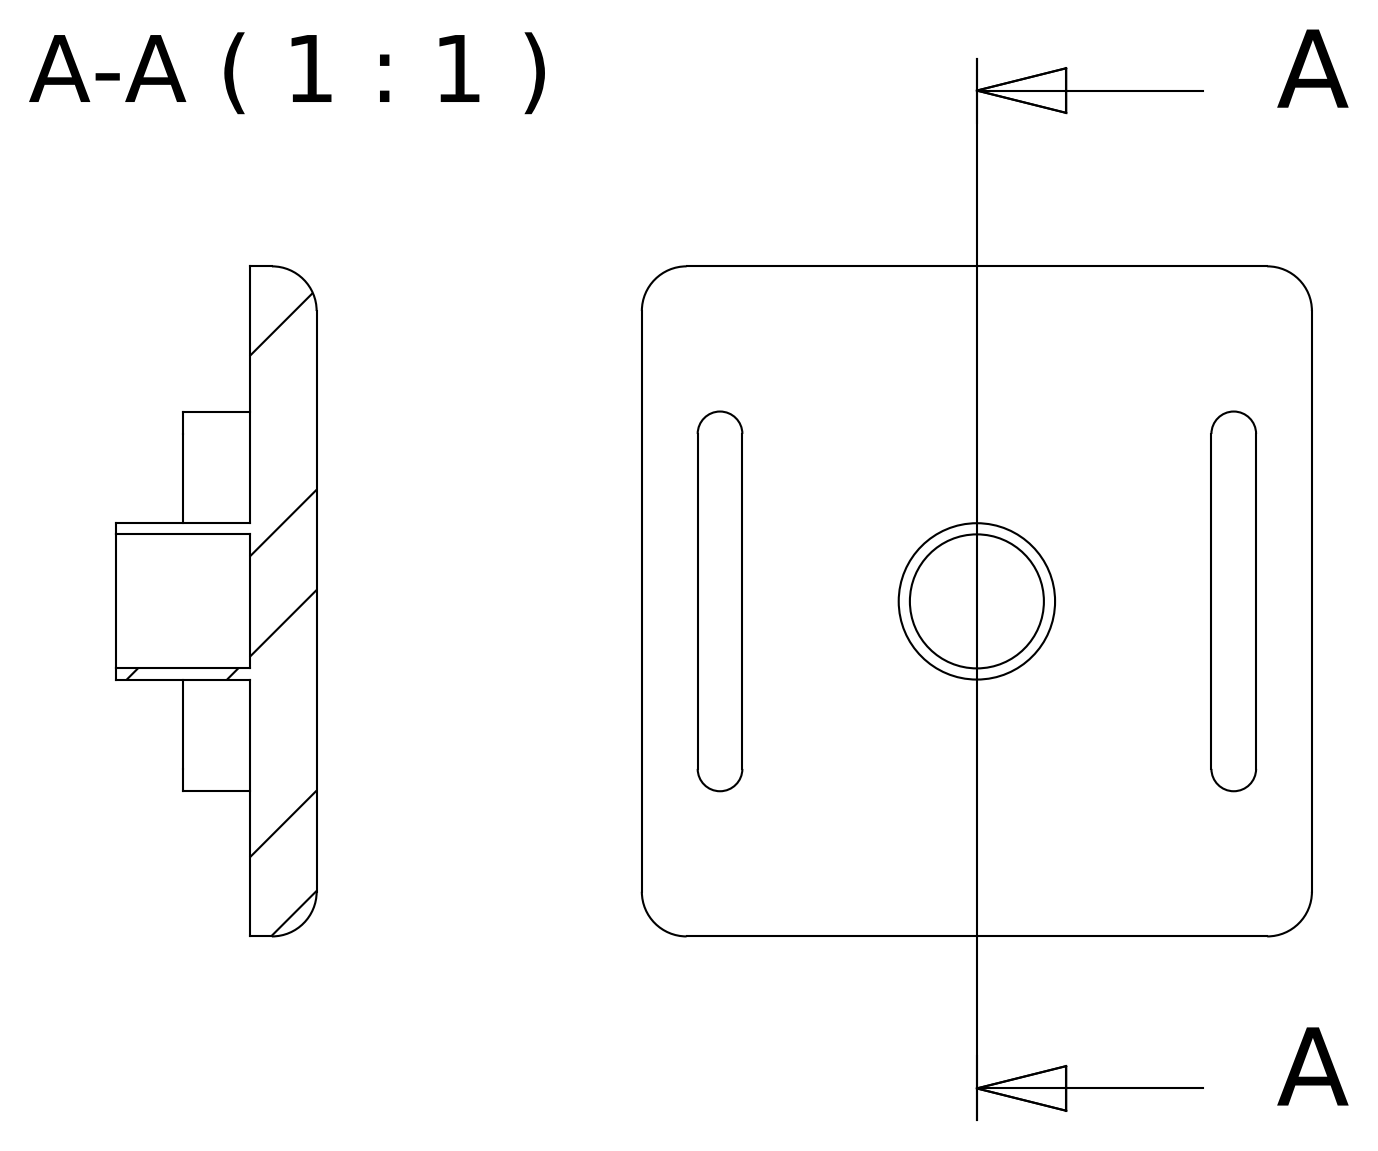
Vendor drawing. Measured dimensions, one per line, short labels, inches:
name: DTPTR0000022
written by: Autodesk Inventor 2016 (AUTOMOTIVE_DESIGN)
unit: in
bodies: 1 solid, 32 faces (14 planar, 14 cylindrical, 4 other)
size: 1.181 × 1.181 × 0.354
volume: 0.174 in³; area: 3.881 in²
holes: 1× ⌀0.236
bosses: 1× ⌀0.276
rounds: 8× R0.079, 4× R0.039
face distances: 0.118, 0.079, 0.906, 0.236, 0.098, 0.177, 1.004, 1.083, 1.181, 0.984
